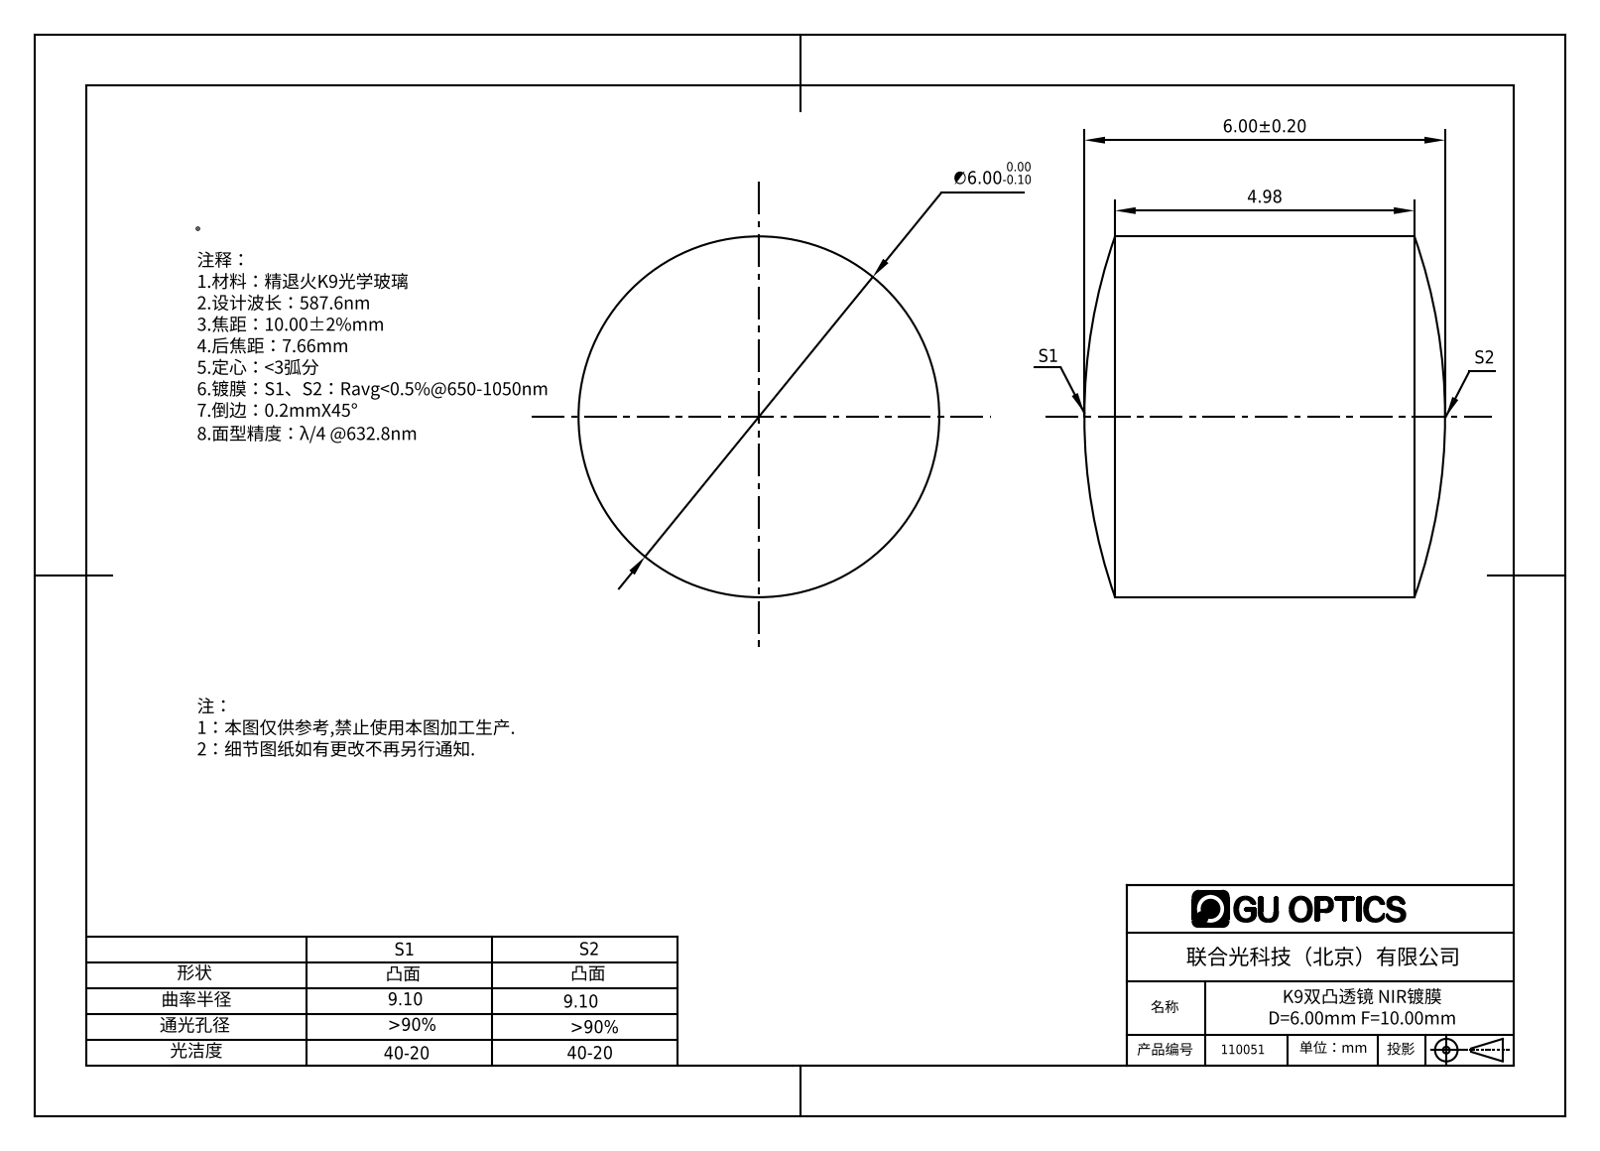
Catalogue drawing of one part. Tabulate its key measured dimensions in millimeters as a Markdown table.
| quantity | value |
| --- | --- |
| part name | 110007 |
| STEP written by | SolidWorks 2016 (CONFIG_CONTROL_DESIGN) |
| units | millimeters |
| bodies | 1 solid, 6 faces (0 planar, 2 cylindrical, 4 other) |
| overall size | 6 × 6 × 6 |
| volume | 155 mm³ |
| surface area | 152 mm² |
| round bosses / shafts (diameter × count) | 6 × 1 |
